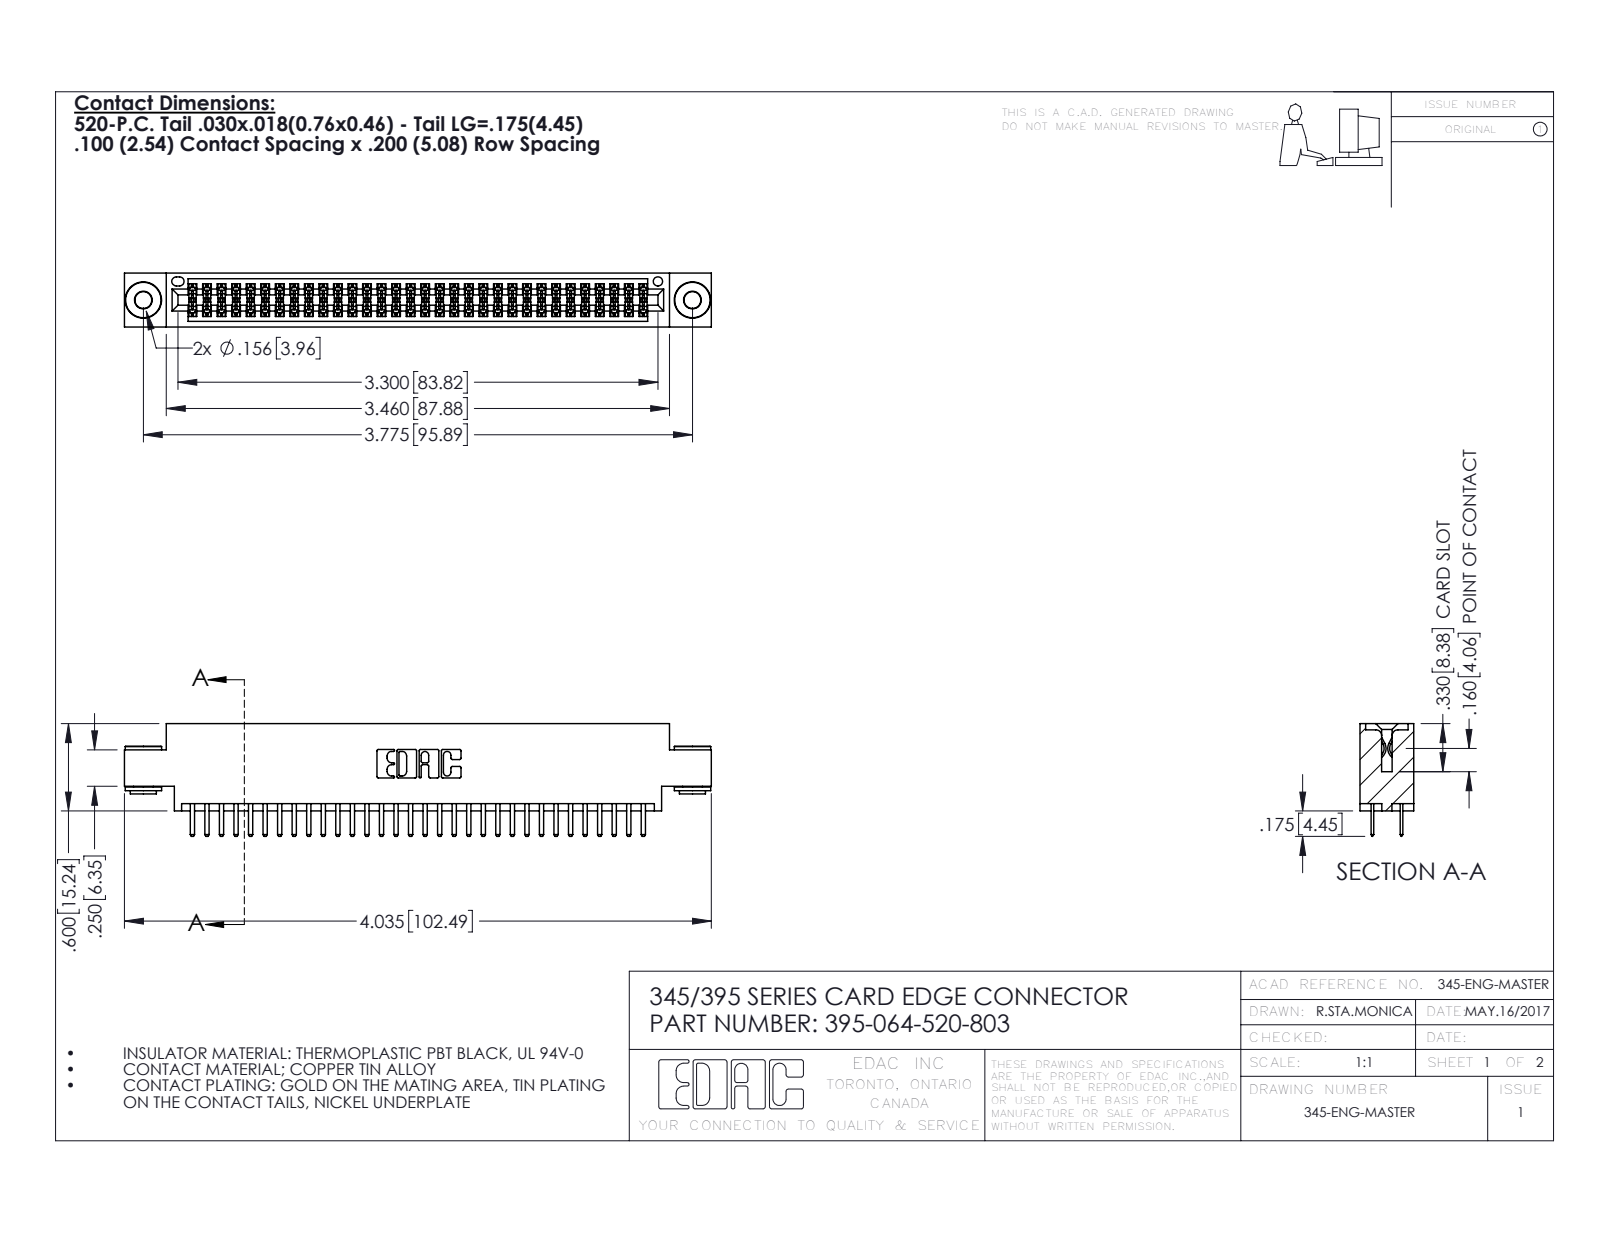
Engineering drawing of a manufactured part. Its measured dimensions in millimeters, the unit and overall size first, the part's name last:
Units: millimetres
Overall size (bounding box): 102.5 × 19.7 × 9.4
Round holes (diameter × count): ⌀2.9 ×2, ⌀4 ×2, ⌀1.6 ×1
Round bosses / shafts (diameter × count): ⌀6.4 ×2, ⌀4.6 ×2, ⌀3.5 ×2
Partial cylindrical surfaces — rounded edges, fillets, slot ends (radius × count): R0.2 ×96, R0.3 ×68, R0.3 ×22, R0.2 ×6, R0.8 ×6, R0.7 ×3, R0.4 ×2, R0.5 ×2
Main face-to-face distances: 1.8, 7.6, 9.4, 5.1, 2.5, 6.9, 0.6, 5.7, 4.4, 0.6
Hole centre spacings: 6.9, 89.9, 95.9
Volume: 9 730 mm³ · Surface area: 14 500 mm²
Bodies: 67 solids, 3624 faces (2334 planar, 1282 cylindrical, 8 other)
Part name (STEP PRODUCT): 345-250-002_345-250-002-102; 395-064-520-803; 345-292-001_345-293-120; 345 Part_0.170 Offset - 0.156 Dia-TH
STEP written by: SolidWorks 2016 (CONFIG_CONTROL_DESIGN)
